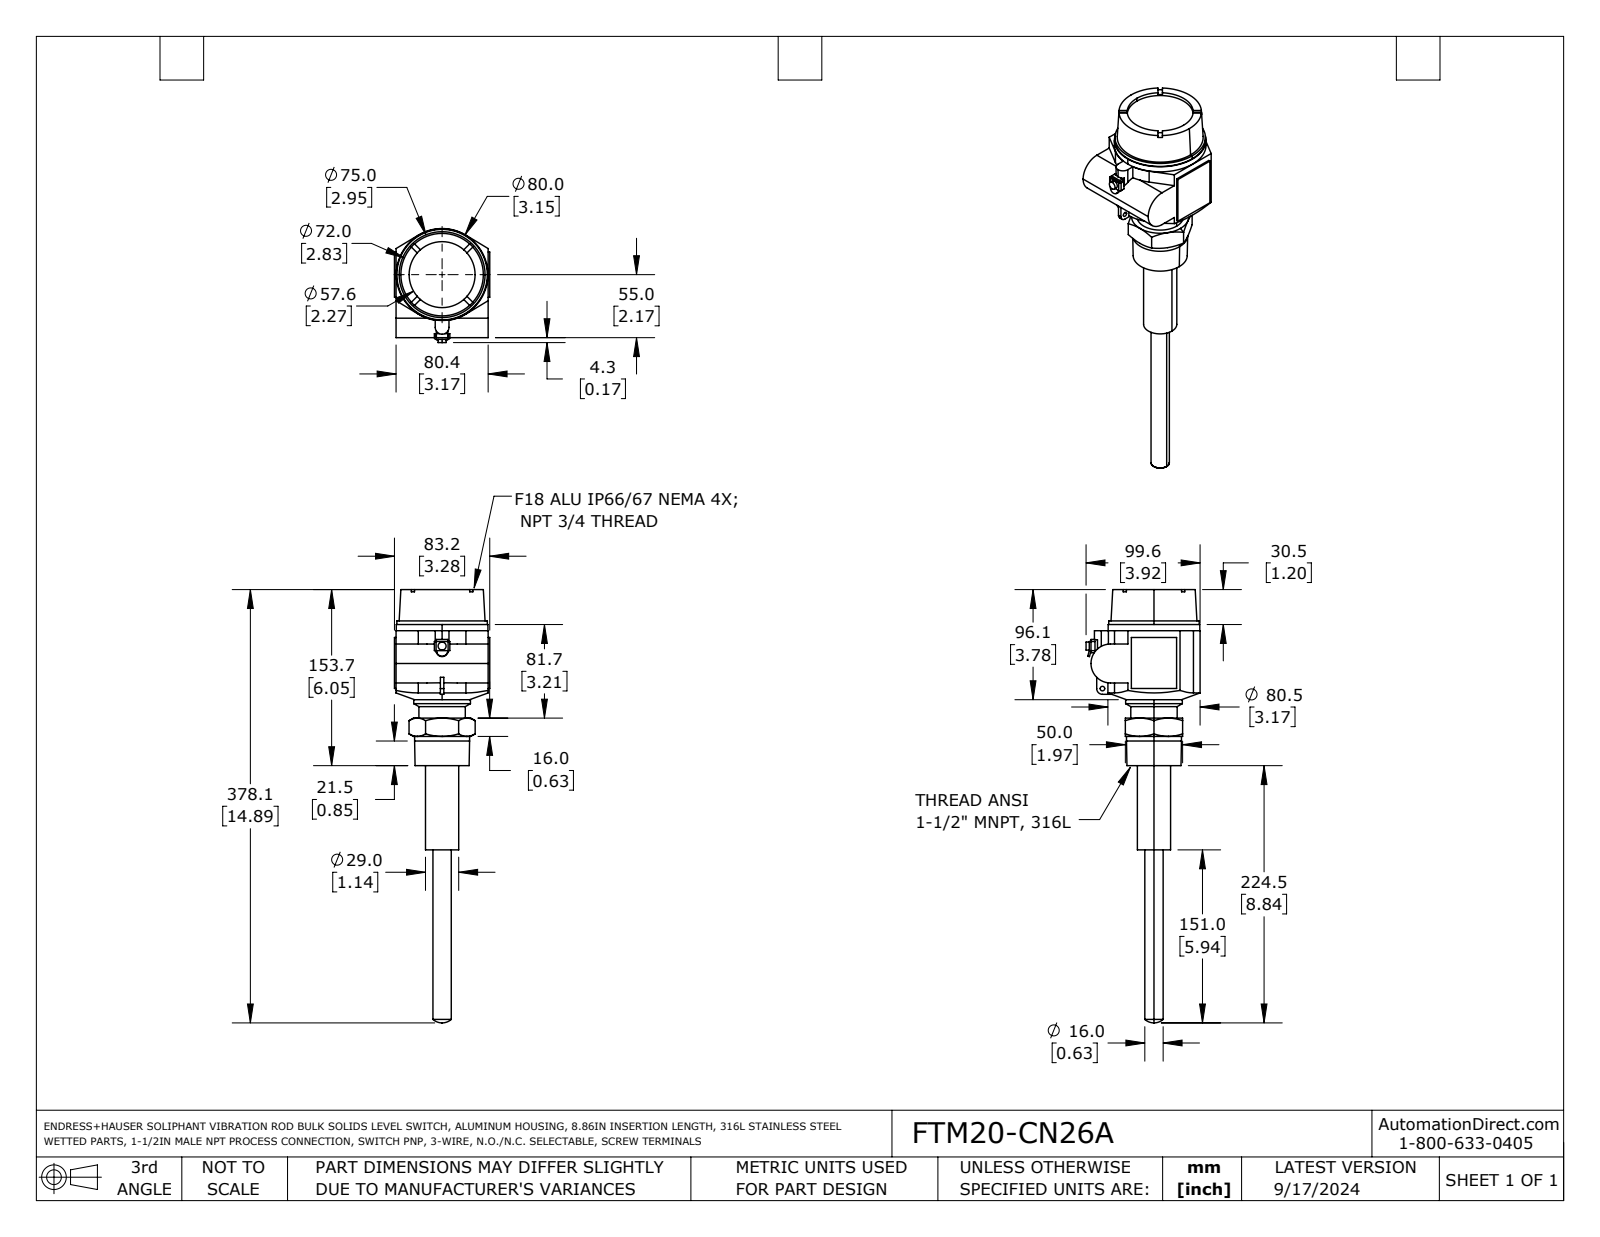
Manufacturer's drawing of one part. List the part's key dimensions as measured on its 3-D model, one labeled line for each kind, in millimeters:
Part name (STEP PRODUCT): FTM20-CN26A
STEP written by: SolidWorks 2021 (CONFIG_CONTROL_DESIGN)
Units: millimetres
Bodies: 1 solid, 151 faces (88 planar, 36 cylindrical, 27 other)
Overall size (bounding box): 378.2 × 99.5 × 83.2
Volume: 702 200 mm³ · Surface area: 64 120 mm²
Round holes (diameter × count): ⌀4 ×1, ⌀57.6 ×1
Round bosses / shafts (diameter × count): ⌀80 ×1, ⌀79 ×1, ⌀49.5 ×1, ⌀48 ×1, ⌀40.5 ×1, ⌀29 ×1, ⌀16 ×1, ⌀7 ×1
Partial cylindrical surfaces — rounded edges, fillets, slot ends (radius × count): R1.5 ×3, R5 ×2, R6 ×1, R17 ×1, R40.3 ×1
Main face-to-face distances: 1.4, 81.8, 83.2, 80.4, 3, 50, 150.6, 153.6, 80.5, 41.5
